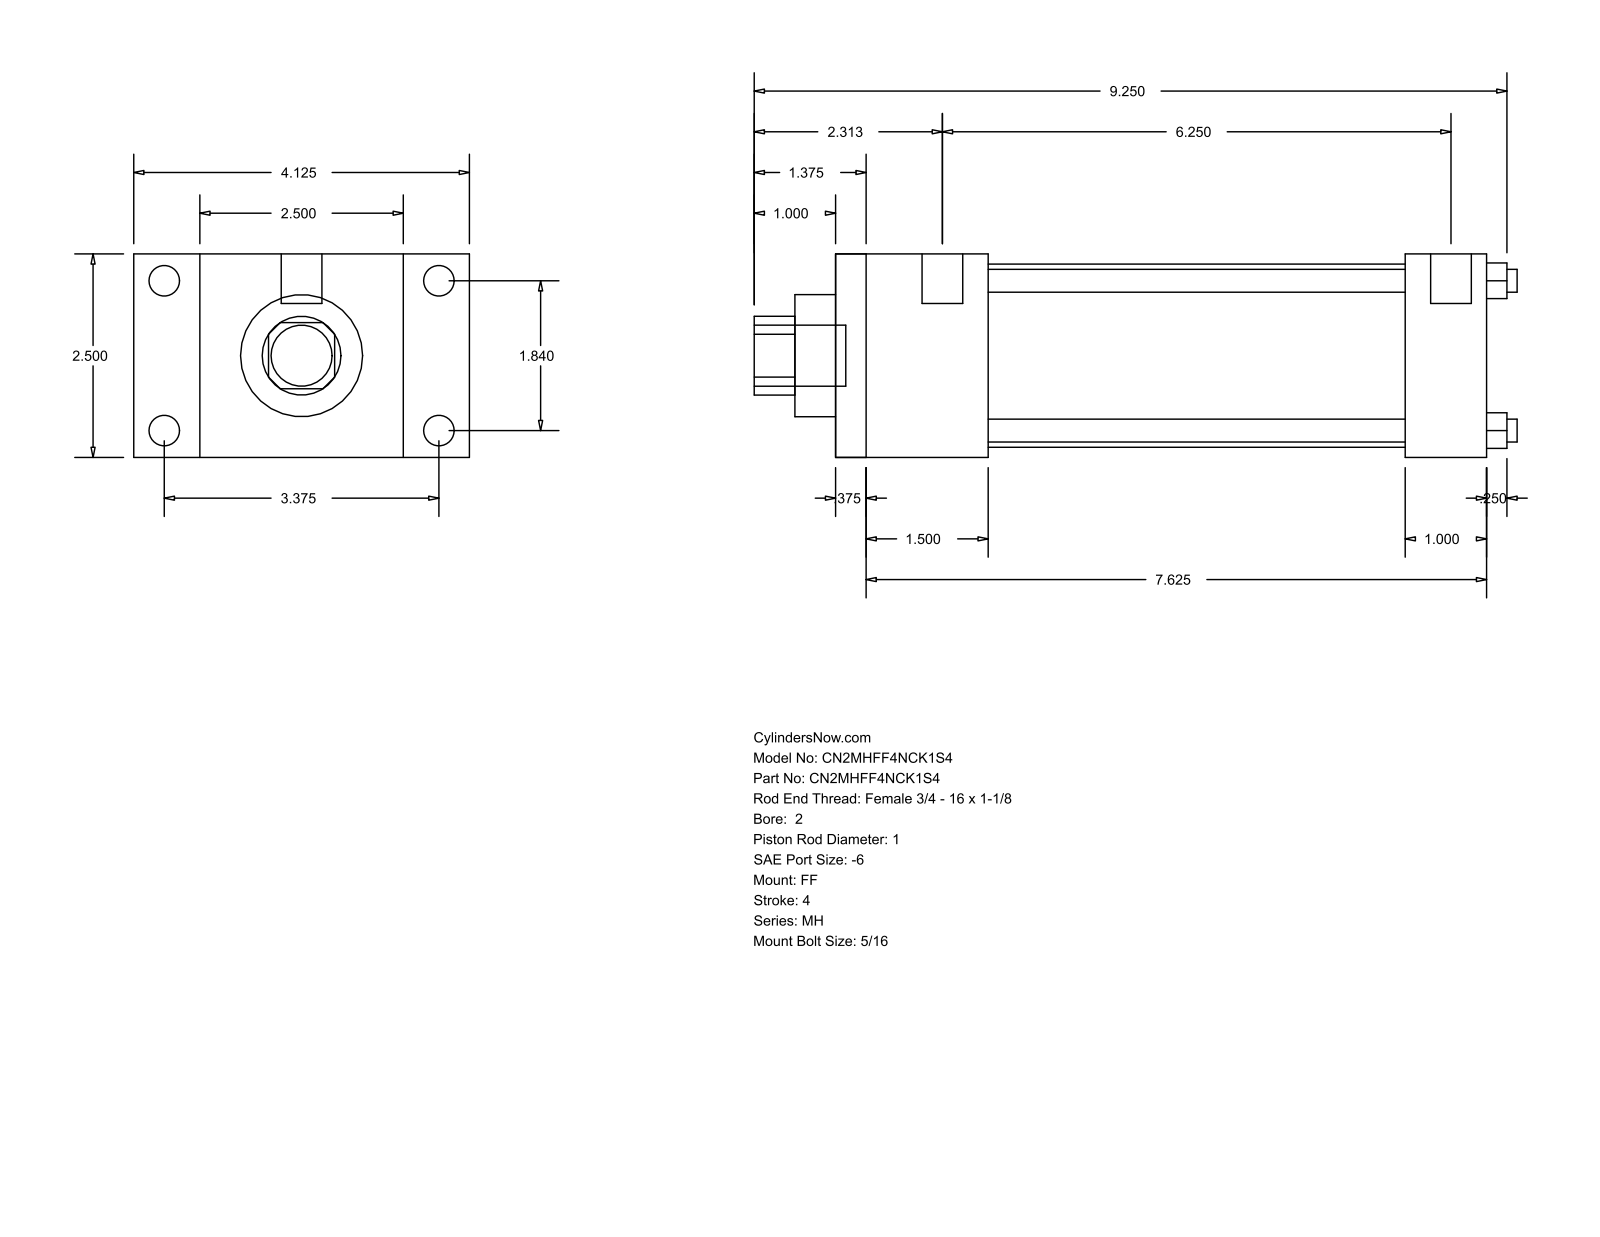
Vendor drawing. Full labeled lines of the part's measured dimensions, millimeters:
Part name (STEP PRODUCT): MH_FF__0200_1
STEP written by: GSSL Pune (CONFIG_CONTROL_DESIGN)
Units: millimetres
Bodies: 0 solids, 92 faces (64 planar, 28 cylindrical, 0 other)
Overall size (bounding box): 238.12 × 104.78 × 63.5
Round holes (diameter × count): ⌀7.14 ×4, ⌀25.4 ×1, ⌀38.1 ×1, ⌀57.15 ×1
Round bosses / shafts (diameter × count): ⌀9.53 ×4, ⌀5.56 ×4, ⌀12.7 ×2, ⌀19.05 ×1
Partial cylindrical surfaces — rounded edges, fillets, slot ends (radius × count): R12.29 ×1
Main face-to-face distances: 63.5, 203.2, 9.52, 193.68, 20.64, 25.4, 47.63, 177.8, 38.11, 168.28
Hole centre spacings: 33.05, 46.74, 66.1
